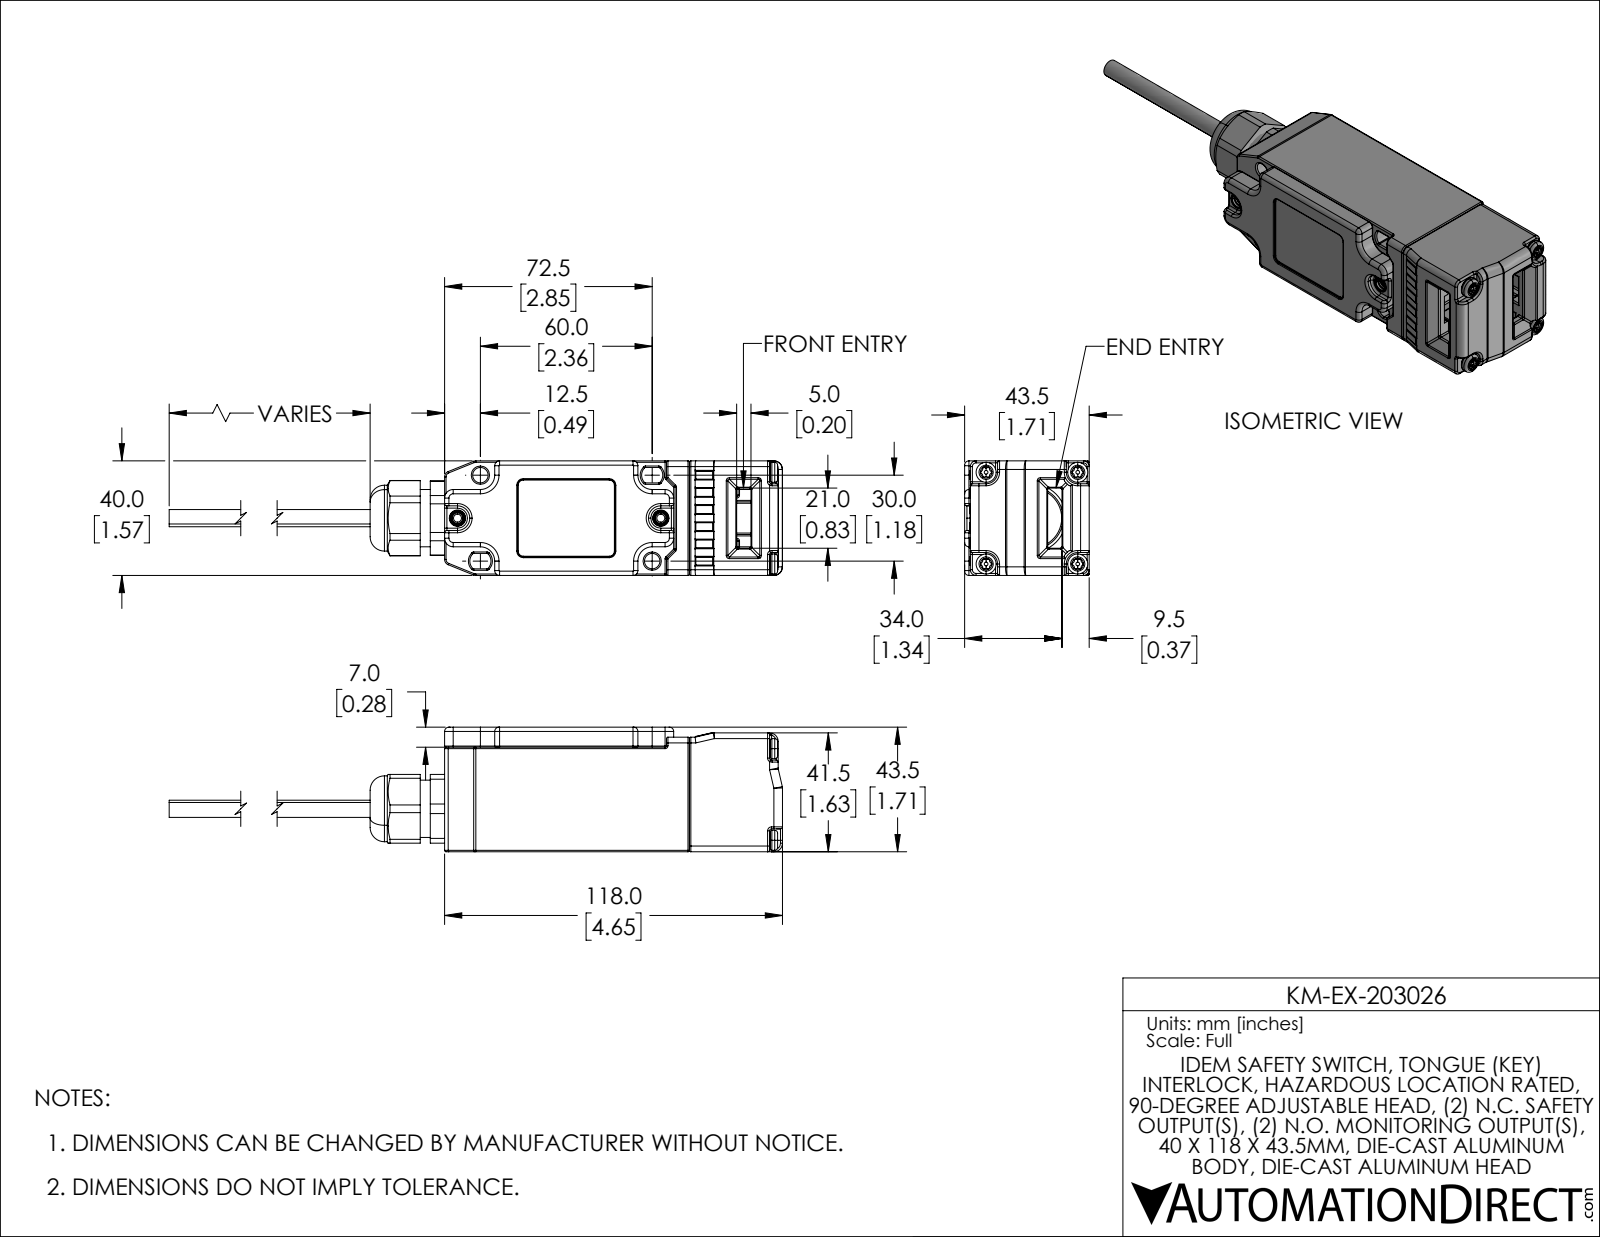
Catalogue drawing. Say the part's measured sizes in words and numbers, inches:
The part is named "KM-EX-203026". Its 3-D file was written by "SolidWorks 2021 (AUTOMOTIVE_DESIGN)". It is 12 solids with 2556 faces: 584 planar, 1005 cylindrical and 967 other. Overall it measures 7.953 by 1.713 by 1.575 inches. Its volume is 5.372 cubic inches and its surface area 95.62 square inches. Round holes: 6 of diameter 0.157, 5 of diameter 0.118, 4 of diameter 0.169, 3 of diameter 0.079, 2 of diameter 0.094, 2 of diameter 0.146, 2 of diameter 0.15, 2 of diameter 0.165, 2 of diameter 0.197, 2 of diameter 0.213, 1 of diameter 0.138, 1 of diameter 0.173. Round bosses or shafts: 6 of diameter 0.244, 4 of diameter 0.276, 4 of diameter 0.138, 4 of diameter 0.051, 2 of diameter 0.252, 2 of diameter 0.236, 1 of diameter 0.906, 1 of diameter 0.197. Partial cylindrical surfaces (rounded edges, fillets, slot ends): 384 of radius 0.02, 53 of radius 0.039, 26 of radius 0.016, 26 of radius 0.031, 20 of radius 0.012, 19 of radius 0.008, 18 of radius 0.028, 18 of radius 0.079. The main face-to-face distances are 1.575, 0.087, 1.488, 0.098, 1.402, 0.102, 0.13, 1.512, 0.173, 1.713. The hole center spacings are 0.891, 1.26, 0.748, 0.339, 0.354, 0.403, 0.413, 0.437.
